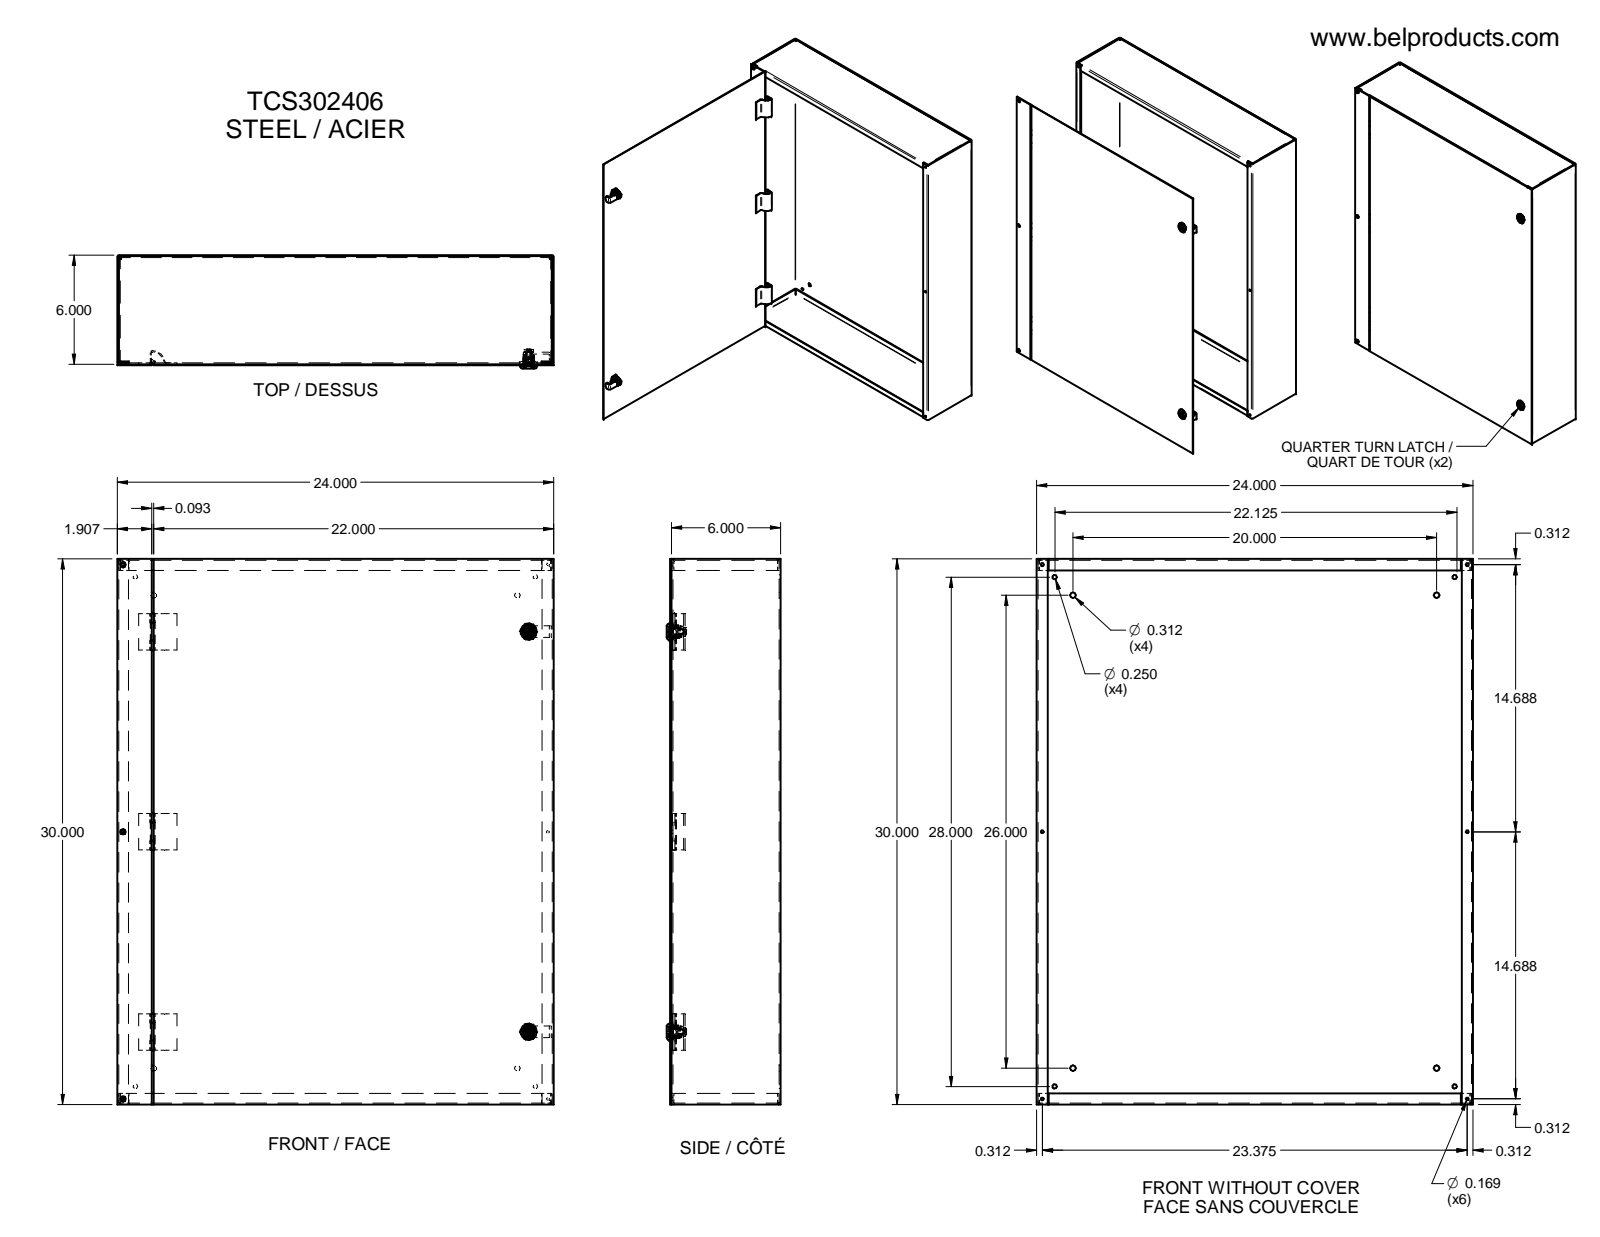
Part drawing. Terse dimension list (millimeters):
name: LOCK AVEC TOURNEVIS TYPE 4-12 SANS CAME; HOSING-oa0; INSERT POUR TOURNEVIS-oa1; NOIX DE FIXATION-oa2 (+8 more)
written by: Unknown (AUTOMOTIVE_DESIGN)
unit: mm
bodies: 29 solids, 1113 faces (557 planar, 274 cylindrical, 282 other)
size: 762 × 609.6 × 158.78
volume: 2 696 000 mm³; area: 2 860 000 mm²
holes: 7× ⌀7.92, 6× ⌀4.29, 4× ⌀6.35, 2× ⌀6.99, 2× ⌀9.1, 2× ⌀11.18, 2× ⌀12.83, 2× ⌀15.8, 2× ⌀17.46, 1× ⌀3.81
bosses: 2× ⌀22.86, 2× ⌀22.61, 2× ⌀15.75, 2× ⌀12.95, 2× ⌀12.62, 2× ⌀12.19, 2× ⌀11.86, 2× ⌀10.08
rounds: 22× R9.53, 16× R0.25, 13× R0.81, 12× R2.72, 4× R9.42, 2× R1.52, 2× R3.05, 2× R6.22
face distances: 1.91, 152.4, 150.49, 154.31, 1.9, 607.69, 760.1, 609.6, 605.78, 762
hole spacings: 24.69, 35.92, 60.61, 332.97, 356.03, 373.06, 534, 552.52
